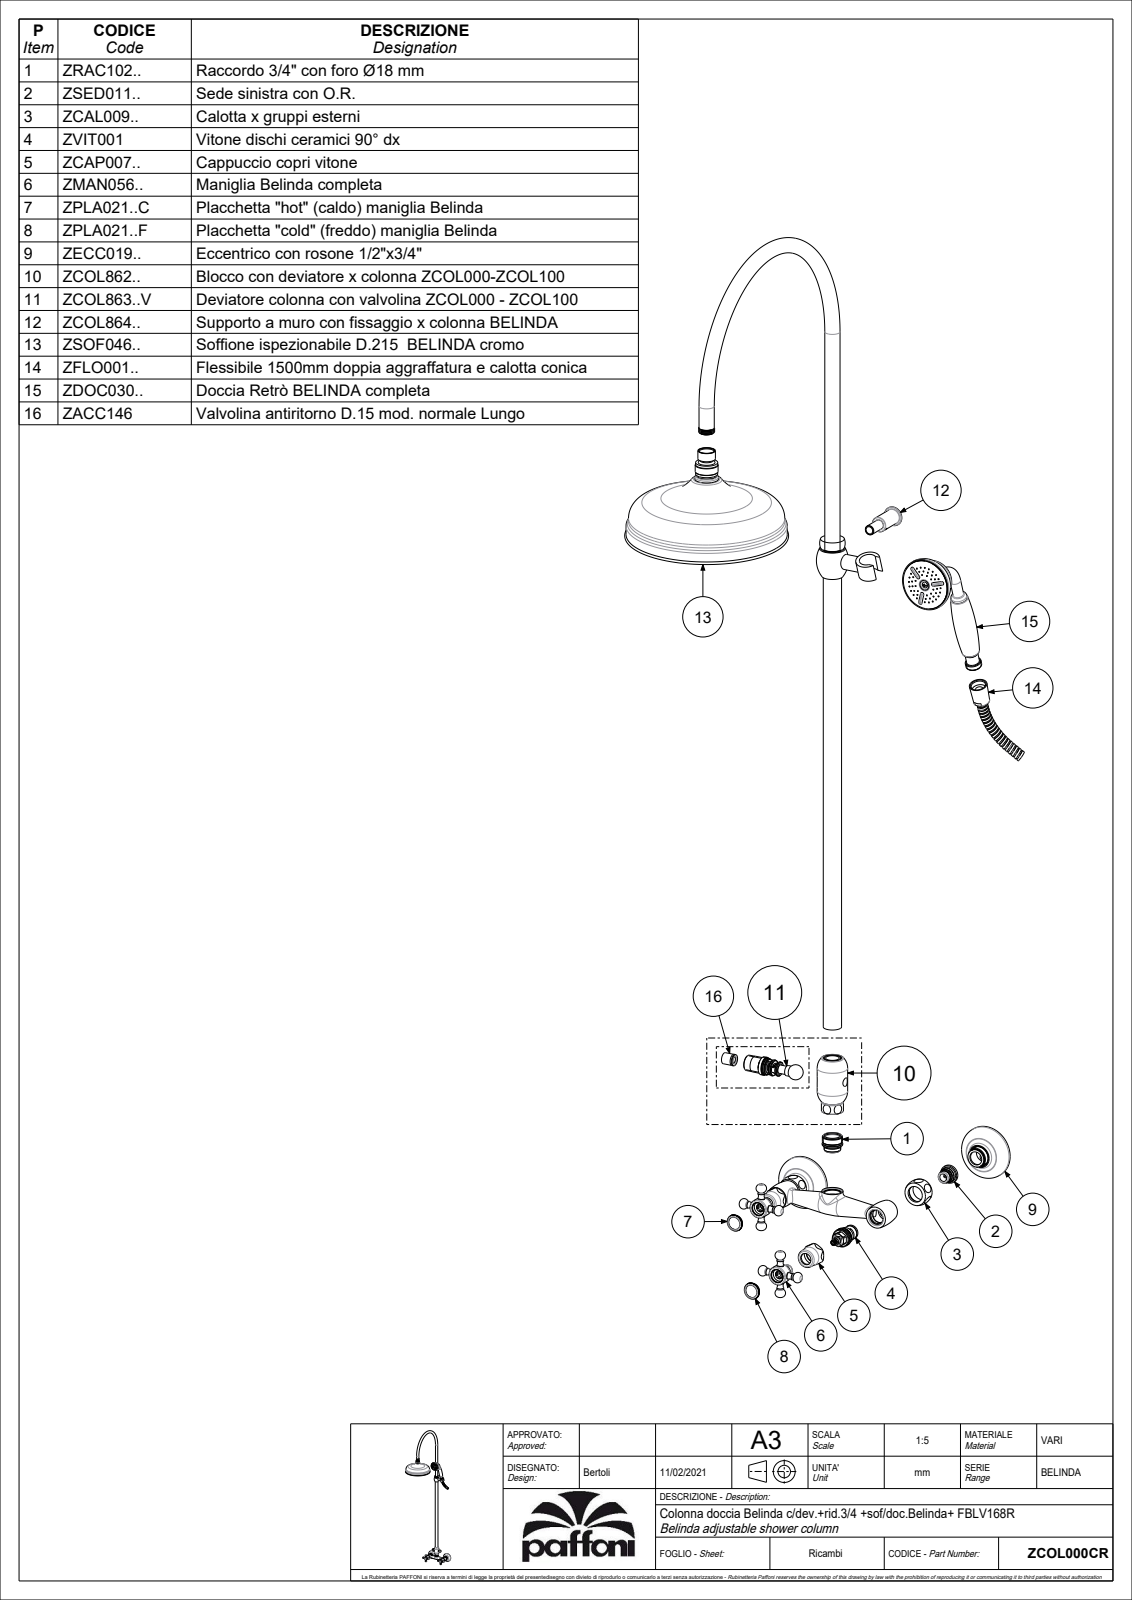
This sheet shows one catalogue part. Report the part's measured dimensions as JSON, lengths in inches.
{"part_name": "3021043TO; 2042273GR; 2092247_AF0; 5002070CR_ASM (+8 more)", "step_written_by": "CREO PARAMETRIC BY PTC INC, 2020044 (CONFIG_CONTROL_DESIGN)", "units": "inches", "bodies": {"solids": 49, "faces": 3282, "planar": 1088, "cylindrical": 1159, "other": 1035}, "overall_size": [49.696, 20.374, 8.661], "volume_in3": 106.7, "surface_area_in2": 785.9, "round_holes": [[0.079, 100], [0.047, 45], [0.748, 5], [0.118, 4], [0.413, 4], [0.433, 4], [0.205, 3], [0.512, 3], [1.004, 3], [0.394, 2], [0.48, 2], [0.571, 2]], "round_bosses_or_shafts": [[0.551, 7], [0.827, 6], [0.512, 5], [0.945, 4], [1.039, 3], [0.807, 3], [0.787, 3], [0.709, 3]], "partial_cylinders_radius": [[0.02, 14], [0.138, 2], [0.433, 2], [0.122, 1], [0.207, 1], [0.211, 1], [0.266, 1], [0.384, 1]], "face_to_face_distances": [0.591, 0.276, 0.02, 2.756, 0.472, 0.079, 0.039, 3.248, 0.217, 6.472], "hole_center_spacings": [0.551, 0.945, 2.244, 0.748, 1.07, 0.955, 1.39, 0.226]}
